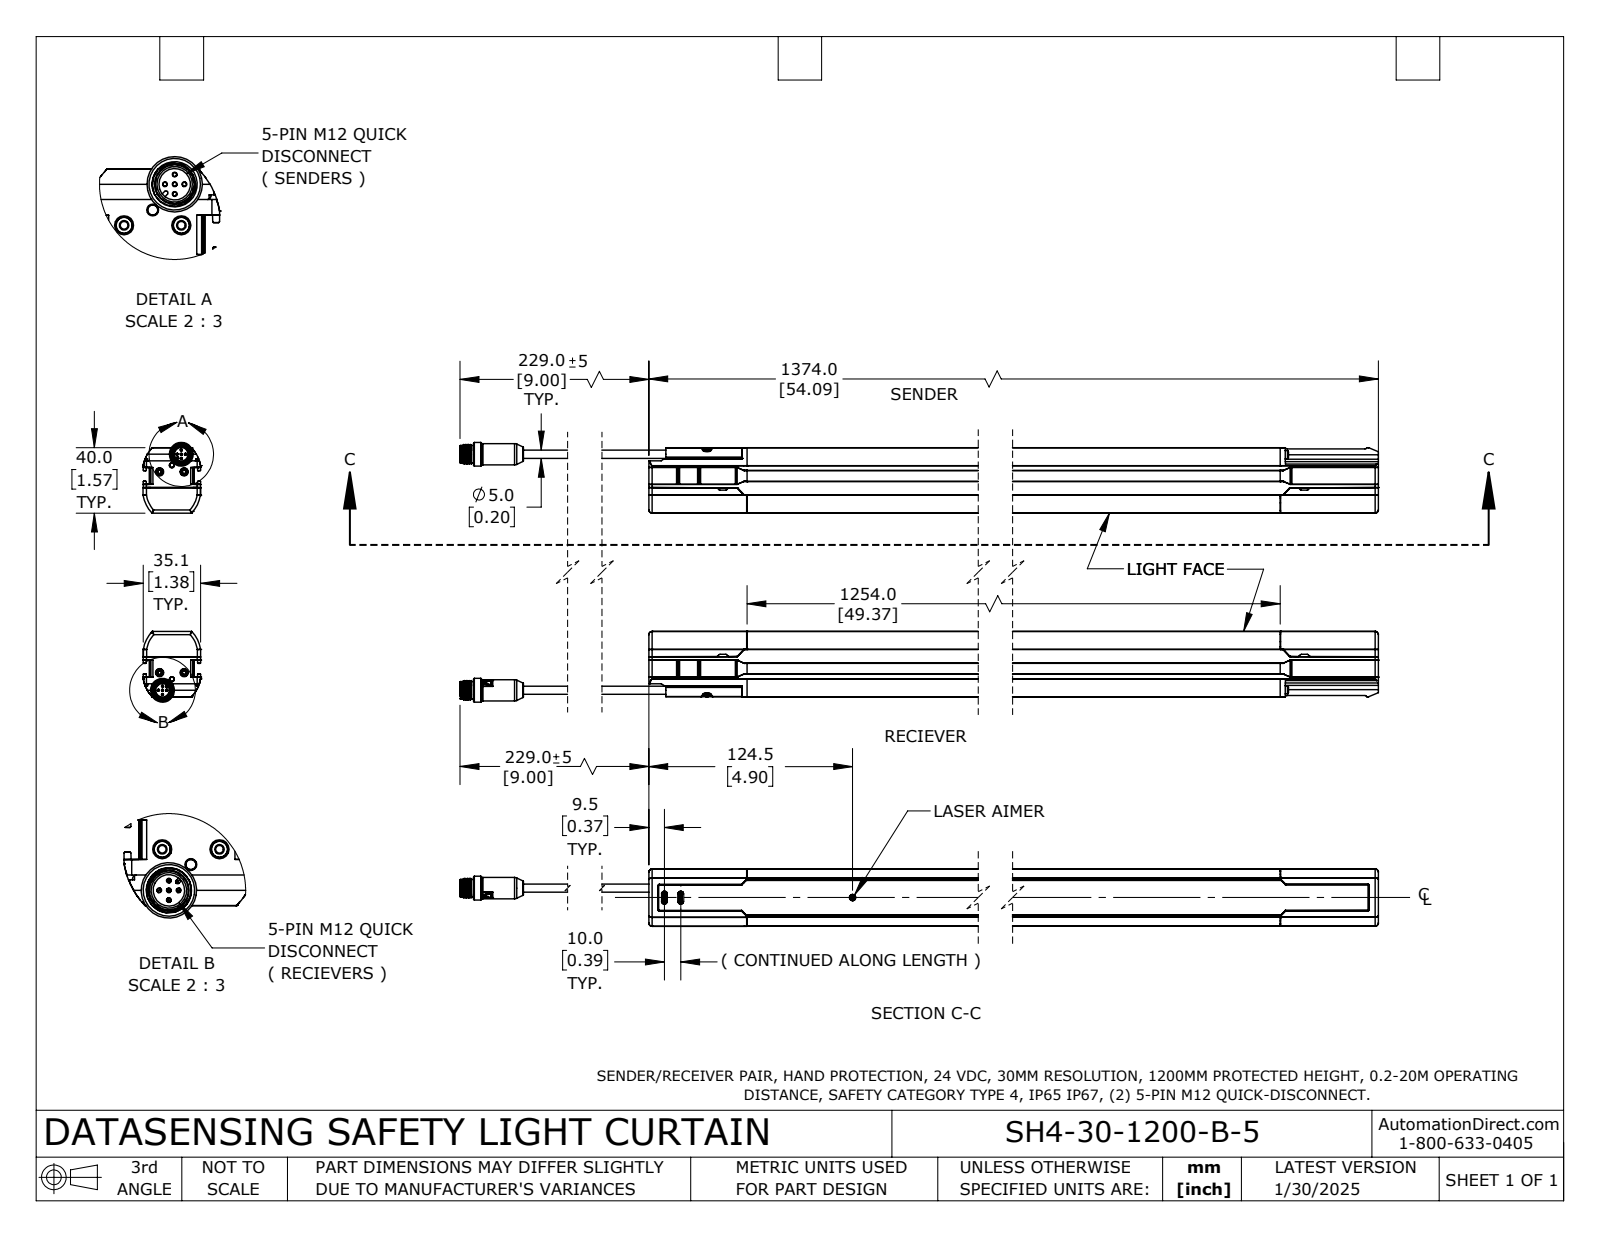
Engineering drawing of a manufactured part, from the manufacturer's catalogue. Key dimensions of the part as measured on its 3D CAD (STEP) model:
Part name (STEP PRODUCT): 957920007
STEP written by: SolidWorks 2024 (AUTOMOTIVE_DESIGN)
Units: inches
Bodies: 4 solids, 2582 faces (1178 planar, 778 cylindrical, 626 other)
Overall size (bounding box): 56.587 × 6.248 × 1.384
Volume: 173.9 in³ · Surface area: 754.5 in²
Round holes (diameter × count): ⌀0.079 ×4, ⌀0.101 ×4, ⌀0.118 ×4, ⌀0.197 ×4, ⌀0.101 ×2, ⌀0.102 ×2, ⌀0.11 ×2, ⌀0.325 ×2, ⌀0.382 ×2, ⌀0.407 ×2, ⌀0.425 ×2
Round bosses / shafts (diameter × count): ⌀0.197 ×10, ⌀0.039 ×10, ⌀0.087 ×8, ⌀0.172 ×4, ⌀0.571 ×2, ⌀0.512 ×2, ⌀0.417 ×2, ⌀0.374 ×2
Partial cylindrical surfaces — rounded edges, fillets, slot ends (radius × count): R0.01 ×164, R0.016 ×66, R0.02 ×50, R0.008 ×36, R0.031 ×20, R0.031 ×12, R0.079 ×12, R0.059 ×10
Main face-to-face distances: 1.496, 4.496, 0.156, 1.222, 3, 5.992, 1.378, 1.067, 4.634, 1.033
Hole centre spacings: 0.866, 5.27, 5.34, 0.429, 0.591, 0.672, 4.831, 4.867
